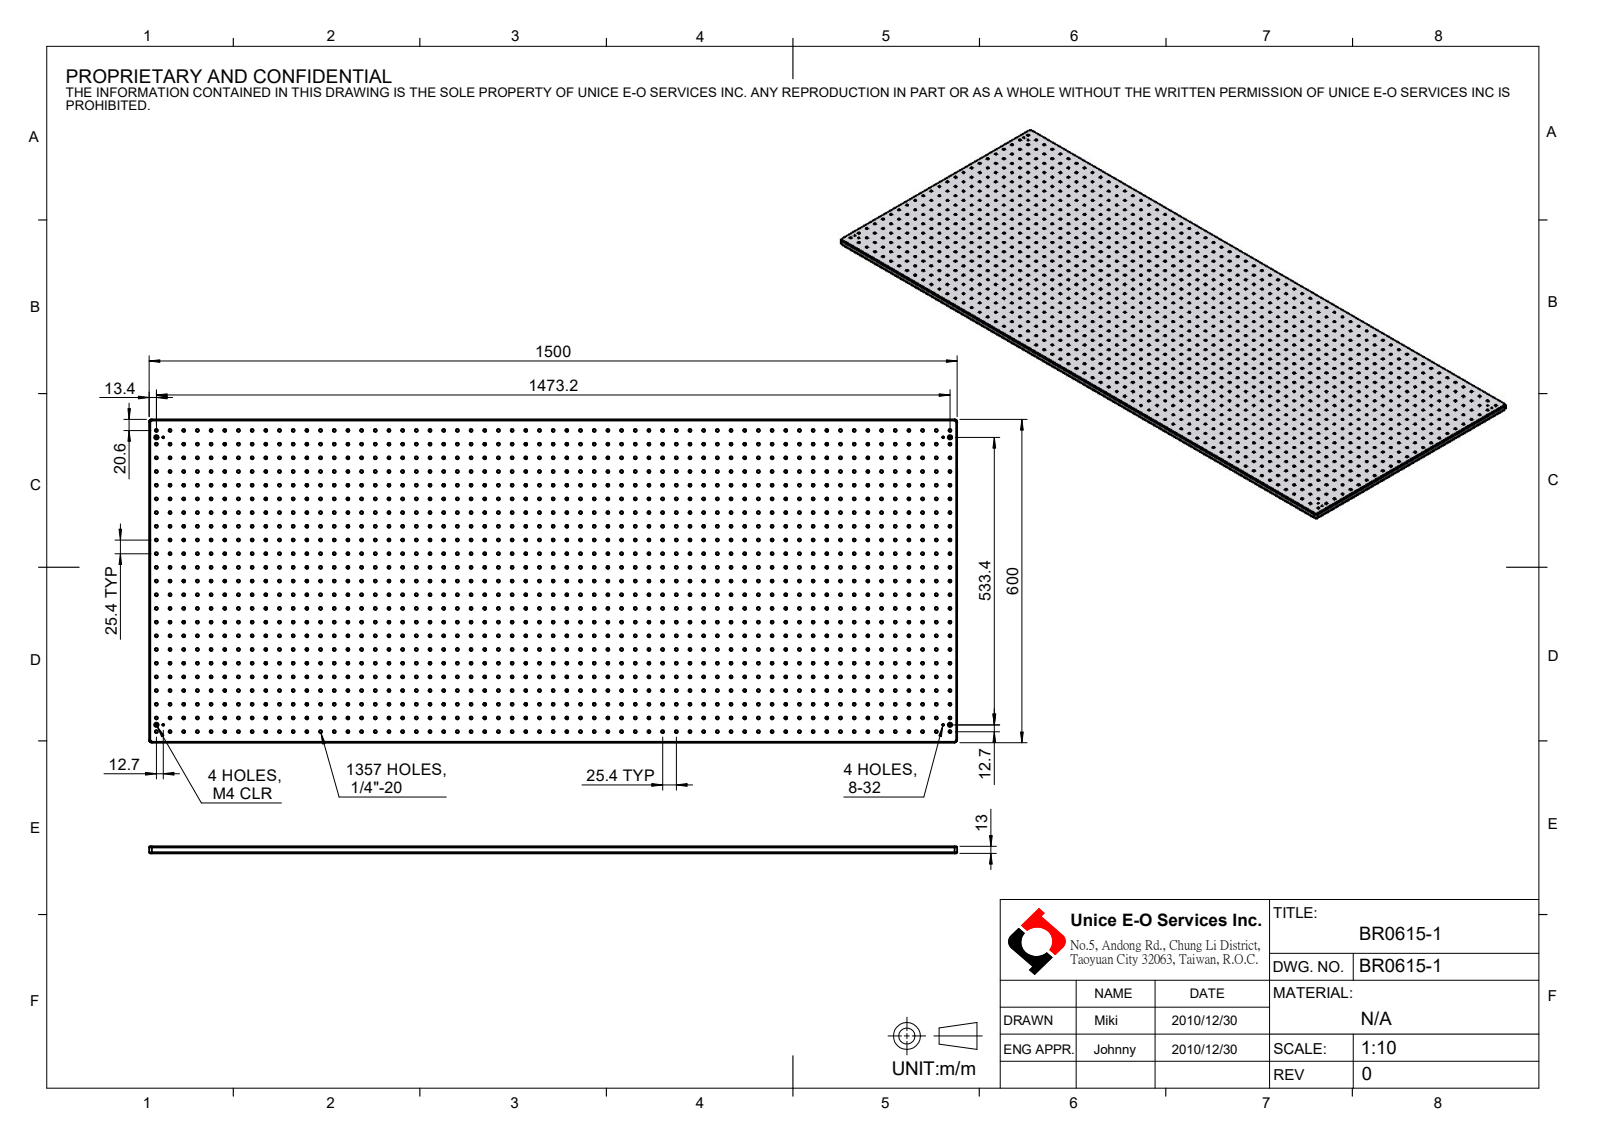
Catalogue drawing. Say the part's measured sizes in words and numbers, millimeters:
The part is named "BR0615-1". Its 3-D file was written by "SolidWorks 2016 (CONFIG_CONTROL_DESIGN)". It is 1 solid with 2768 faces: 10 planar, 2750 cylindrical and 8 other. Overall it measures 1500 by 600 by 13 millimeters. Its volume is 11 330 000 cubic millimeters and its surface area 2 076 000 square millimeters. Round holes: 1357 of diameter 5.11, 4 of diameter 3.45, 4 of diameter 4.5, 4 of diameter 8. Partial cylindrical surfaces (rounded edges, fillets, slot ends): 8 of radius 2, 4 of radius 5. The main face-to-face distances are 13, 600, 1500, 7, 6. The hole center spacings are 25.4, 50.8, 76.2, 101.6, 127, 152.4, 177.8, 203.2.
